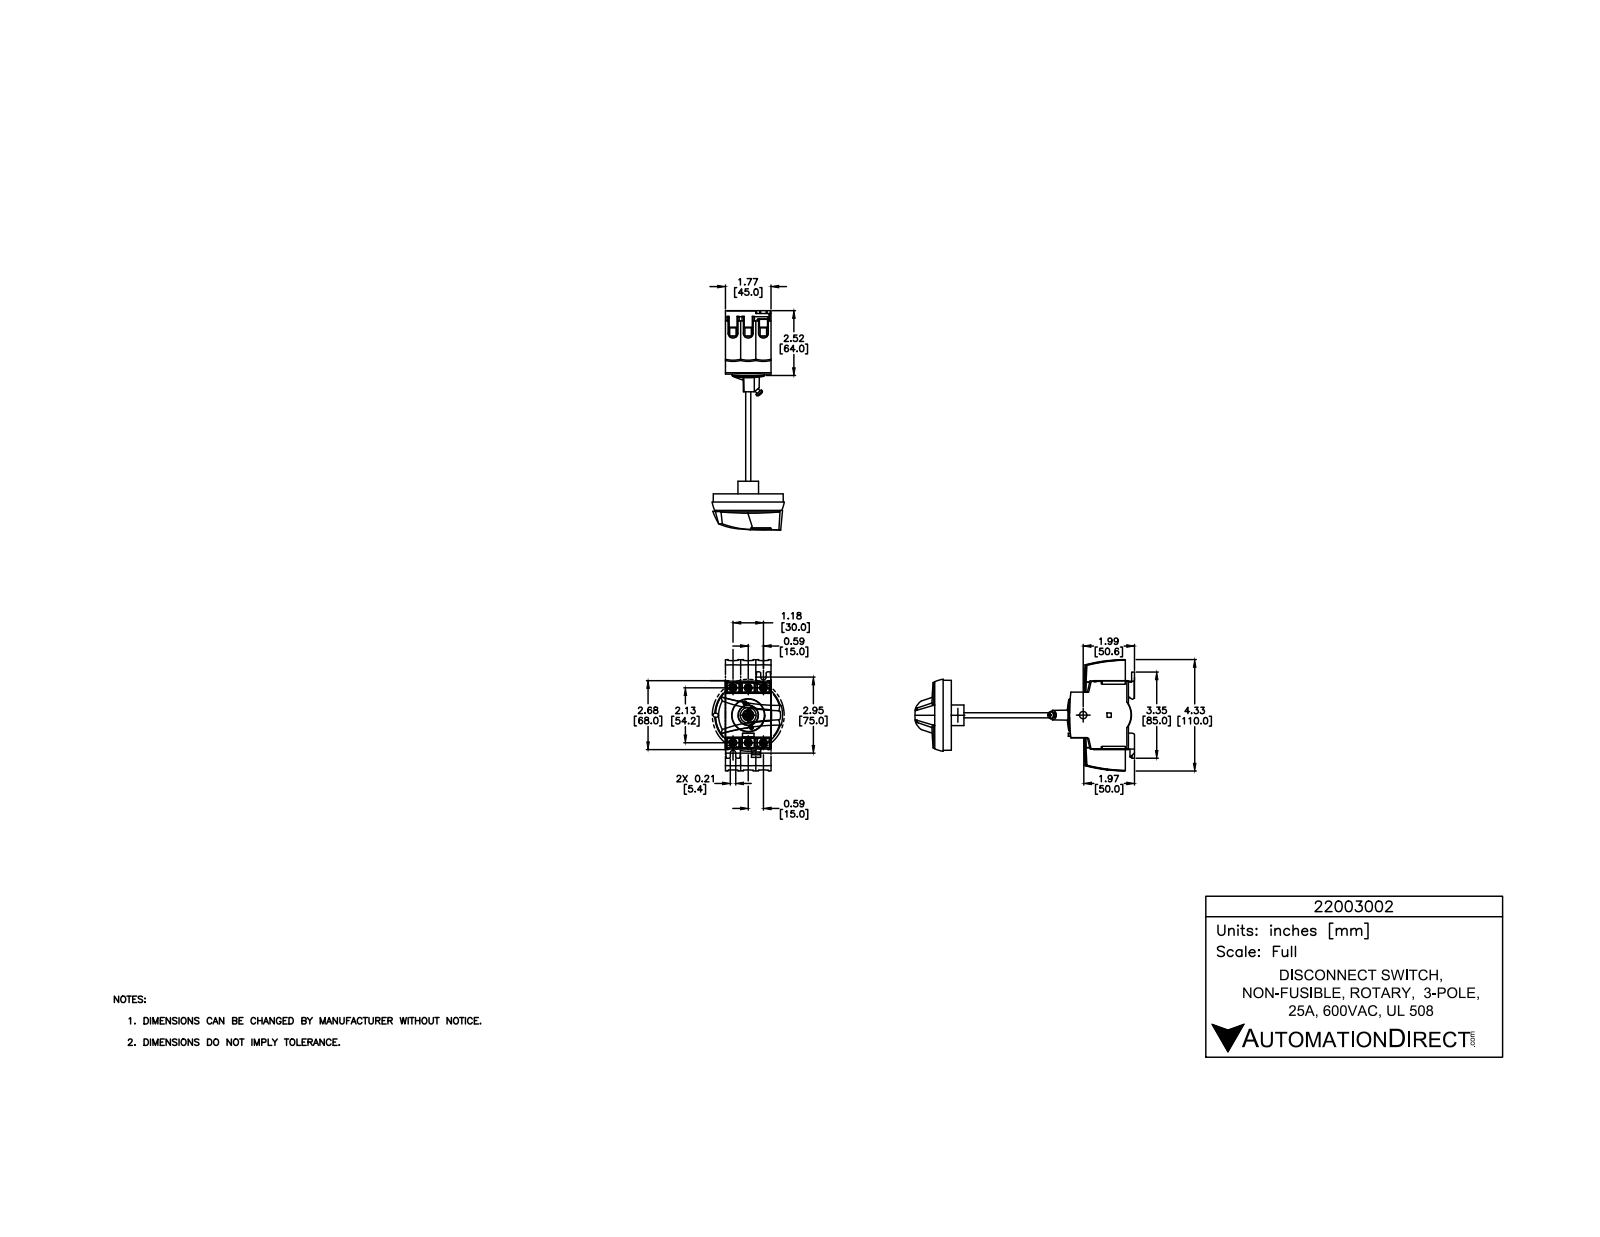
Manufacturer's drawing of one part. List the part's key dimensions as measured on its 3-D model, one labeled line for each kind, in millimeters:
Part name (STEP PRODUCT): 22003002-UL
STEP written by: SolidWorks 2021 (CONFIG_CONTROL_DESIGN)
Units: millimetres
Bodies: 1 solid, 463 faces (389 planar, 50 cylindrical, 24 other)
Overall size (bounding box): 85 × 65.3 × 45
Volume: 155 600 mm³ · Surface area: 25 950 mm²
Round holes (diameter × count): ⌀6.6 ×6, ⌀7.2 ×1, ⌀31.6 ×1
Partial cylindrical surfaces — rounded edges, fillets, slot ends (radius × count): R0.3 ×13, R0.5 ×5, R4.2 ×4, R1 ×3, R2.7 ×2, R3.3 ×1, R9 ×1, R9.4 ×1
Main face-to-face distances: 45, 11, 56, 54.8, 67, 57.9, 15, 65.8, 1.2, 9.8
Hole centre spacings: 15, 31, 56.2, 54.2, 27.1, 30, 62
